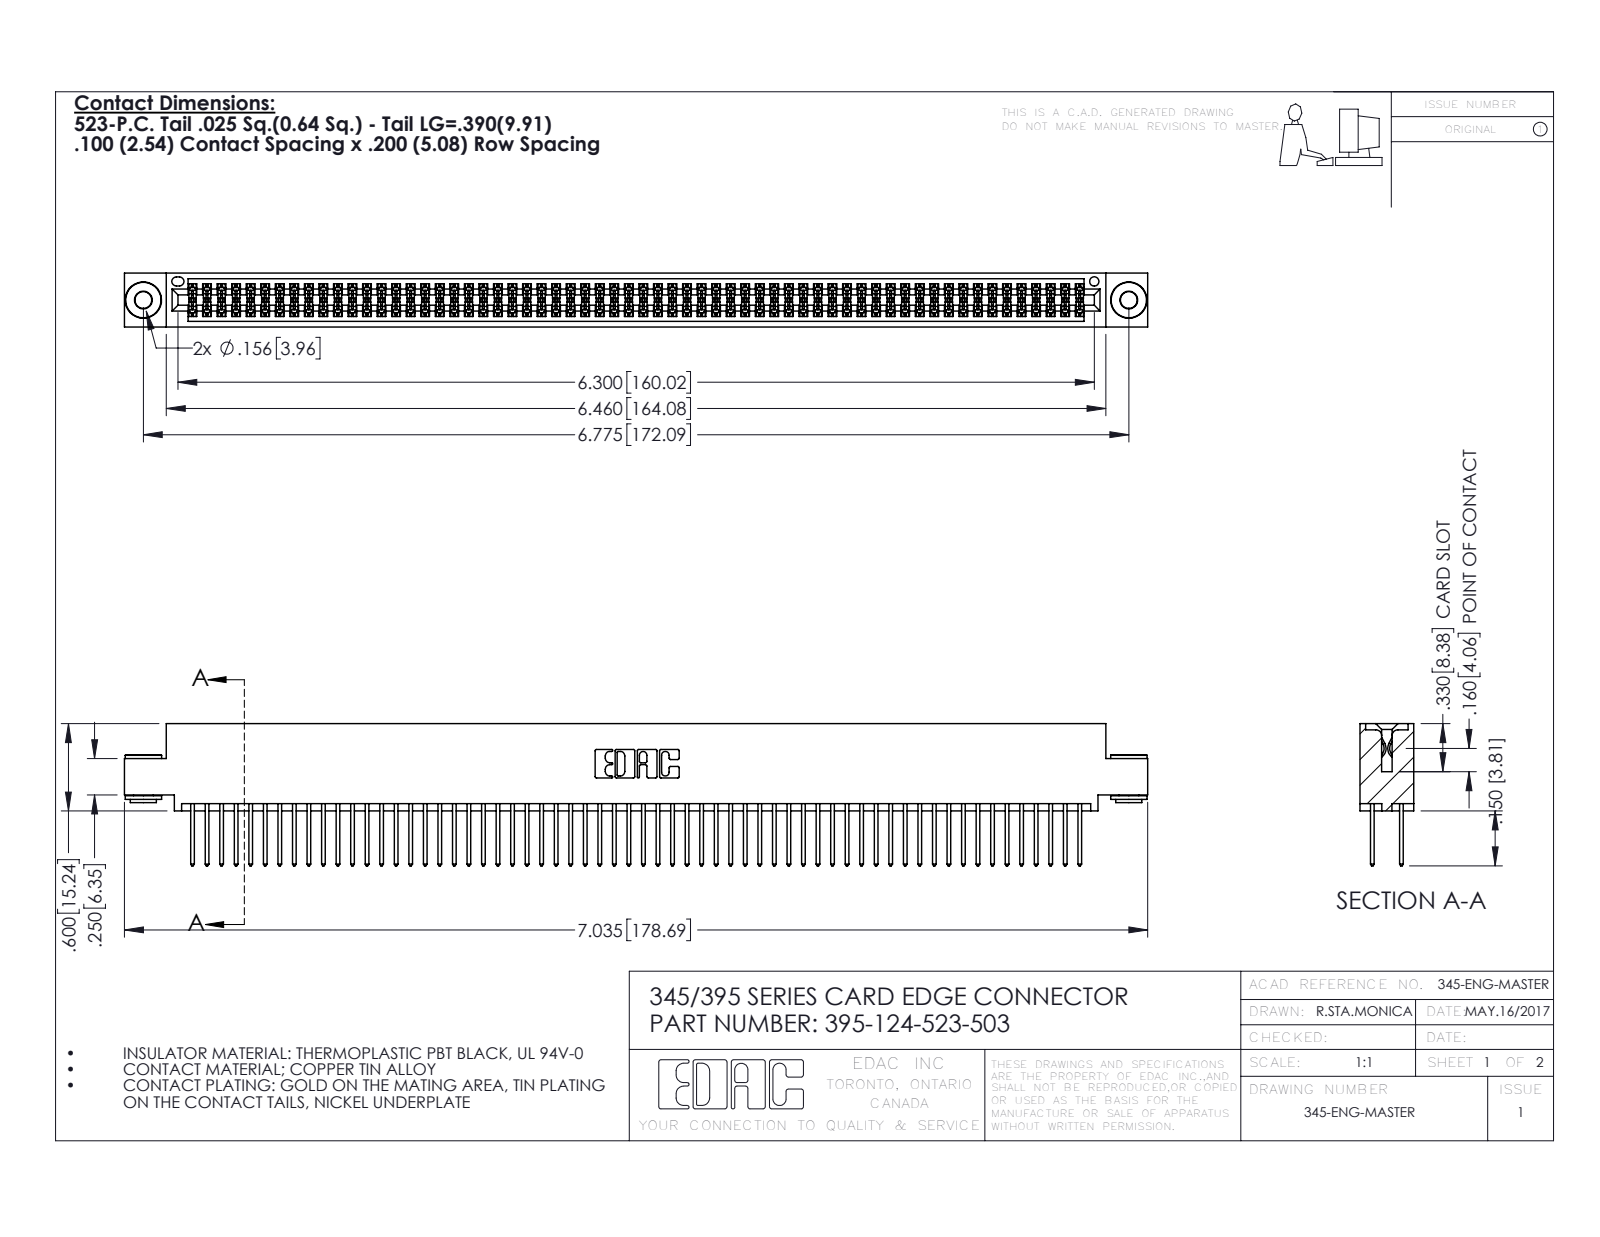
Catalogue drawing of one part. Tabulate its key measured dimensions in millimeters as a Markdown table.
| quantity | value |
| --- | --- |
| part name | 345-250-002_345-250-002-102; 345 Part_0.110 Offset - 0.156 Dia-TH; 395-124-523-503; 345-292-001_345-293-123 |
| STEP written by | SolidWorks 2016 (CONFIG_CONTROL_DESIGN) |
| units | millimeters |
| bodies | 127 solids, 6368 faces (4186 planar, 2174 cylindrical, 8 other) |
| overall size | 178.7 × 24.8 × 9.4 |
| volume | 17 750 mm³ |
| surface area | 28 050 mm² |
| round holes (diameter × count) | 2.9 × 2, 4 × 2, 1.6 × 1 |
| round bosses / shafts (diameter × count) | 6.4 × 2, 4.6 × 2, 3.5 × 2 |
| partial cylindrical surfaces (radius × count) | 0.2 × 186, 0.3 × 124, 0.3 × 22, 0.2 × 6, 0.8 × 6, 0.7 × 3, 0.4 × 2, 0.5 × 2 |
| main face-to-face distances | 1.8, 7.6, 5.1, 0.6, 2.5, 6.9, 9.4, 5.7, 4.4, 3.8 |
| hole center spacings | 6.9, 166.1, 172.1 |
